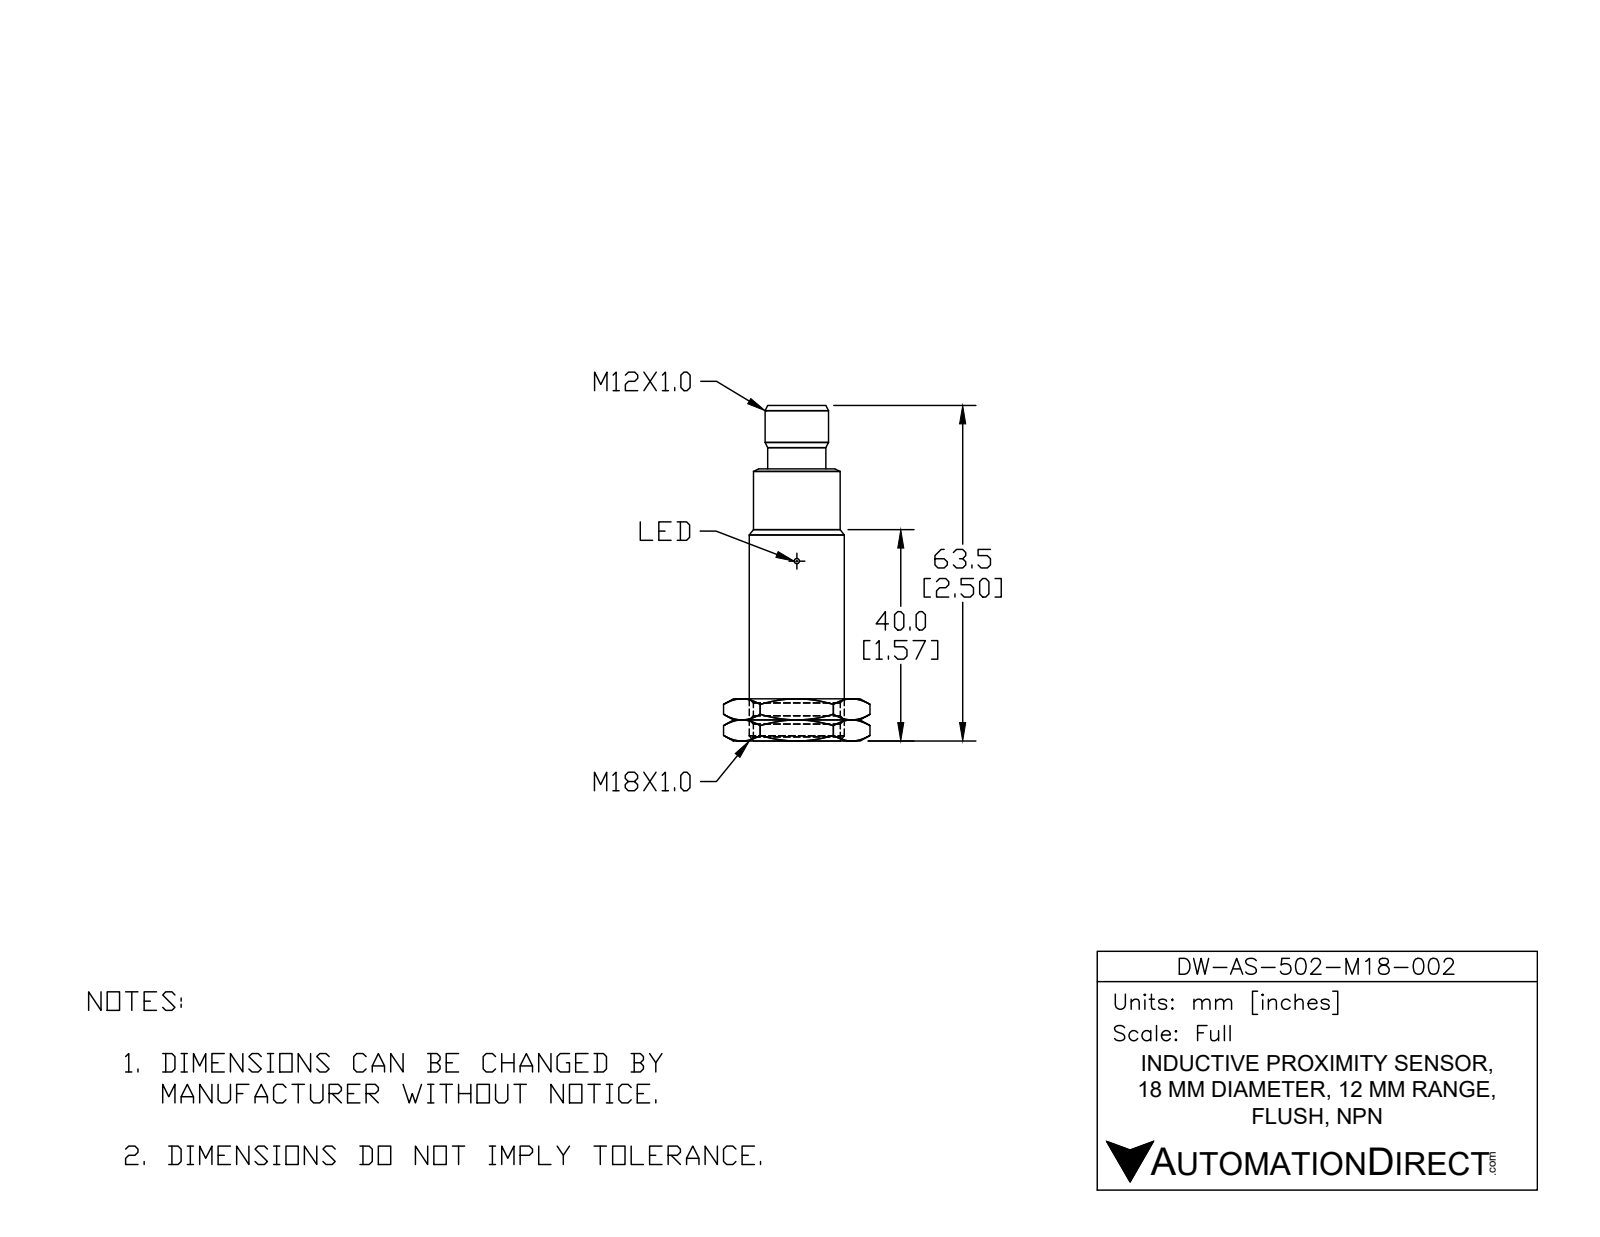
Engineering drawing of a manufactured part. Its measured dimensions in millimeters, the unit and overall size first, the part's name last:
Units: millimetres
Overall size (bounding box): 63.6 × 18 × 18
Round holes (diameter × count): ⌀3 ×2, ⌀8.5 ×1
Round bosses / shafts (diameter × count): ⌀1 ×4, ⌀18 ×1, ⌀16.4 ×1, ⌀12 ×1, ⌀10.5 ×1
Partial cylindrical surfaces — rounded edges, fillets, slot ends (radius × count): R0.6 ×2, R4.9 ×1
Main face-to-face distances: 50.5, 54.9, 4.4, 63.6, 13.1, 8.7, 1.1, 41.5, 9, 13.4
Volume: 13 300 mm³ · Surface area: 4 126 mm²
Bodies: 1 solid, 38 faces (8 planar, 20 cylindrical, 10 other)
Part name (STEP PRODUCT): DW-AS-502-M18-002
STEP written by: SolidWorks 2017 (AUTOMOTIVE_DESIGN)
